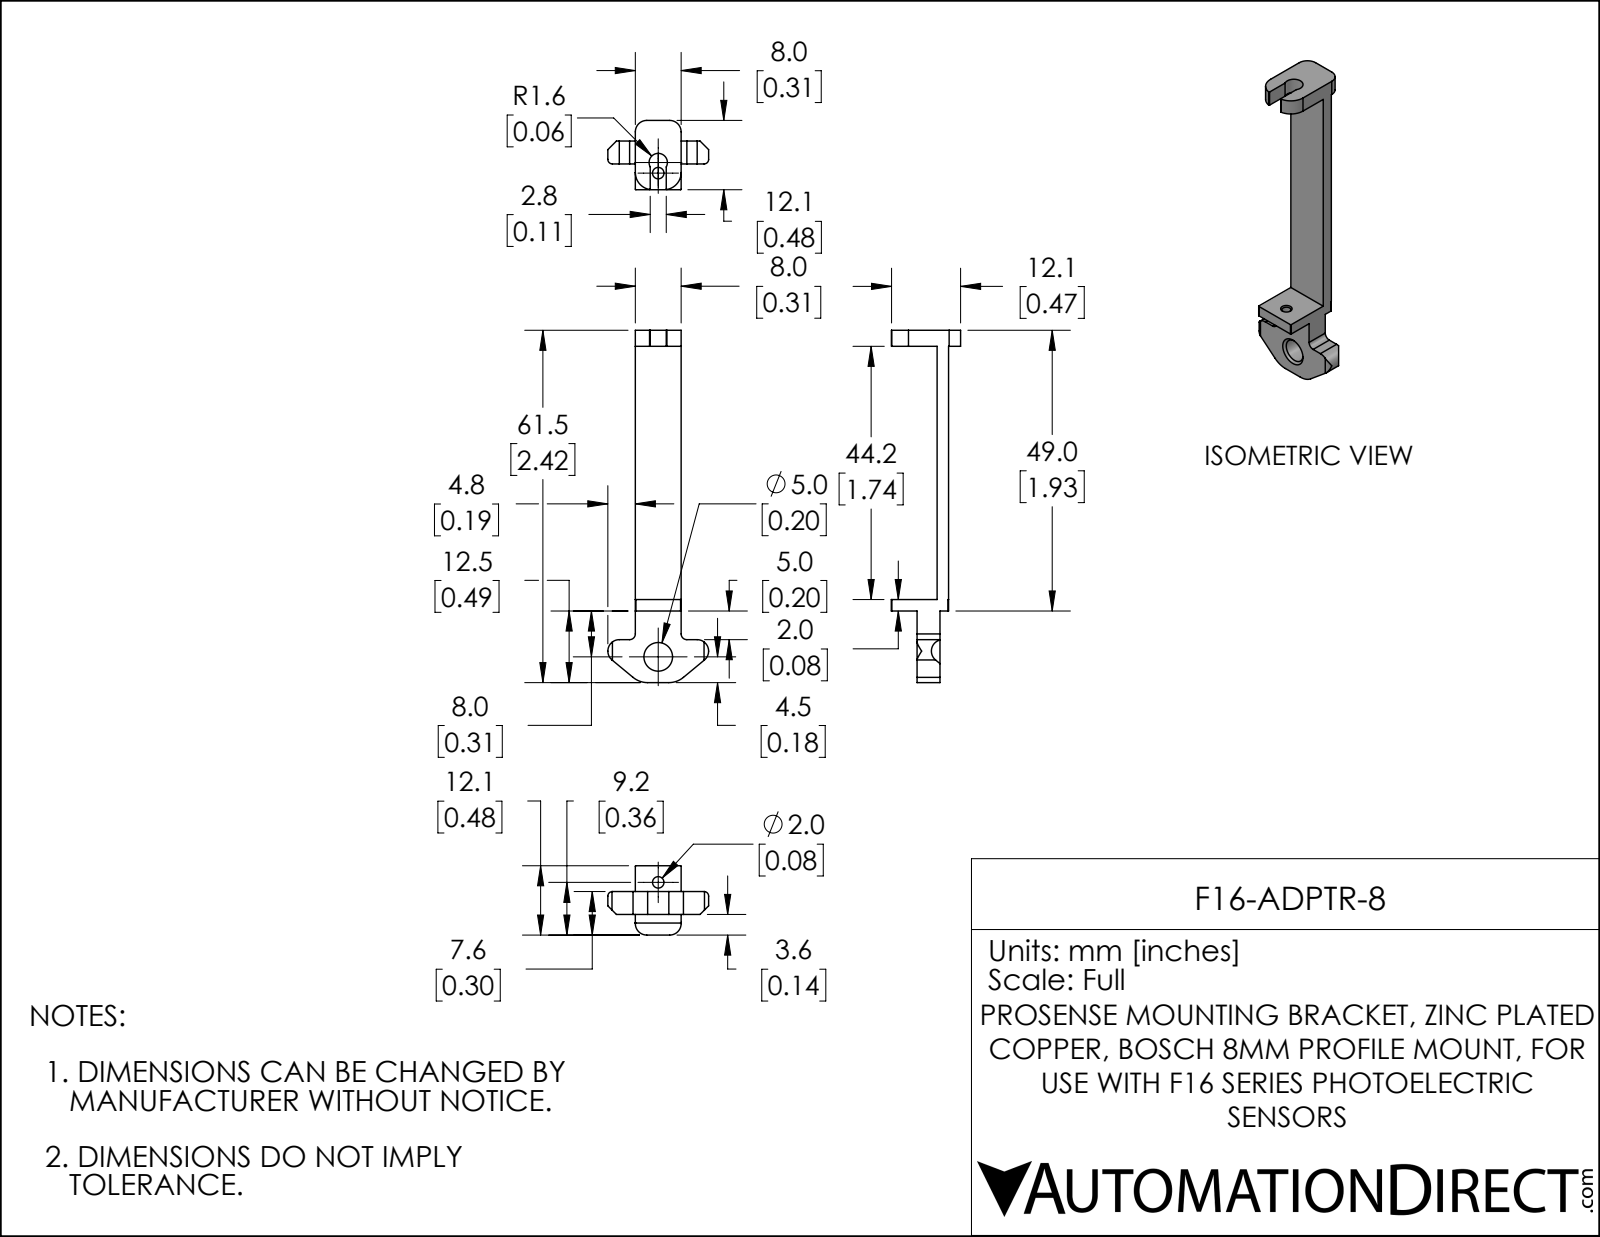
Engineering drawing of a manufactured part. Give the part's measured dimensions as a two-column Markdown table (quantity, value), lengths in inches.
| quantity | value |
| --- | --- |
| part name | F16-ADPTR-8 |
| STEP written by | SolidWorks 2019 (CONFIG_CONTROL_DESIGN) |
| units | inches |
| bodies | 1 solid, 50 faces (25 planar, 21 cylindrical, 4 other) |
| overall size | 2.421 × 0.693 × 0.476 |
| volume | 0.097 in³ |
| surface area | 2.807 in² |
| round holes (diameter × count) | 0.062 × 1, 0.163 × 1 |
| partial cylindrical surfaces (radius × count) | 0.004 × 6, 0.079 × 4, 0.031 × 2, 0.039 × 2, 0.118 × 2, 0.157 × 2, 0.063 × 1 |
| main face-to-face distances | 0.079, 0.315, 0.217, 0.138, 0.059, 0.02, 0.157, 0.11, 1.85, 1.74 |
